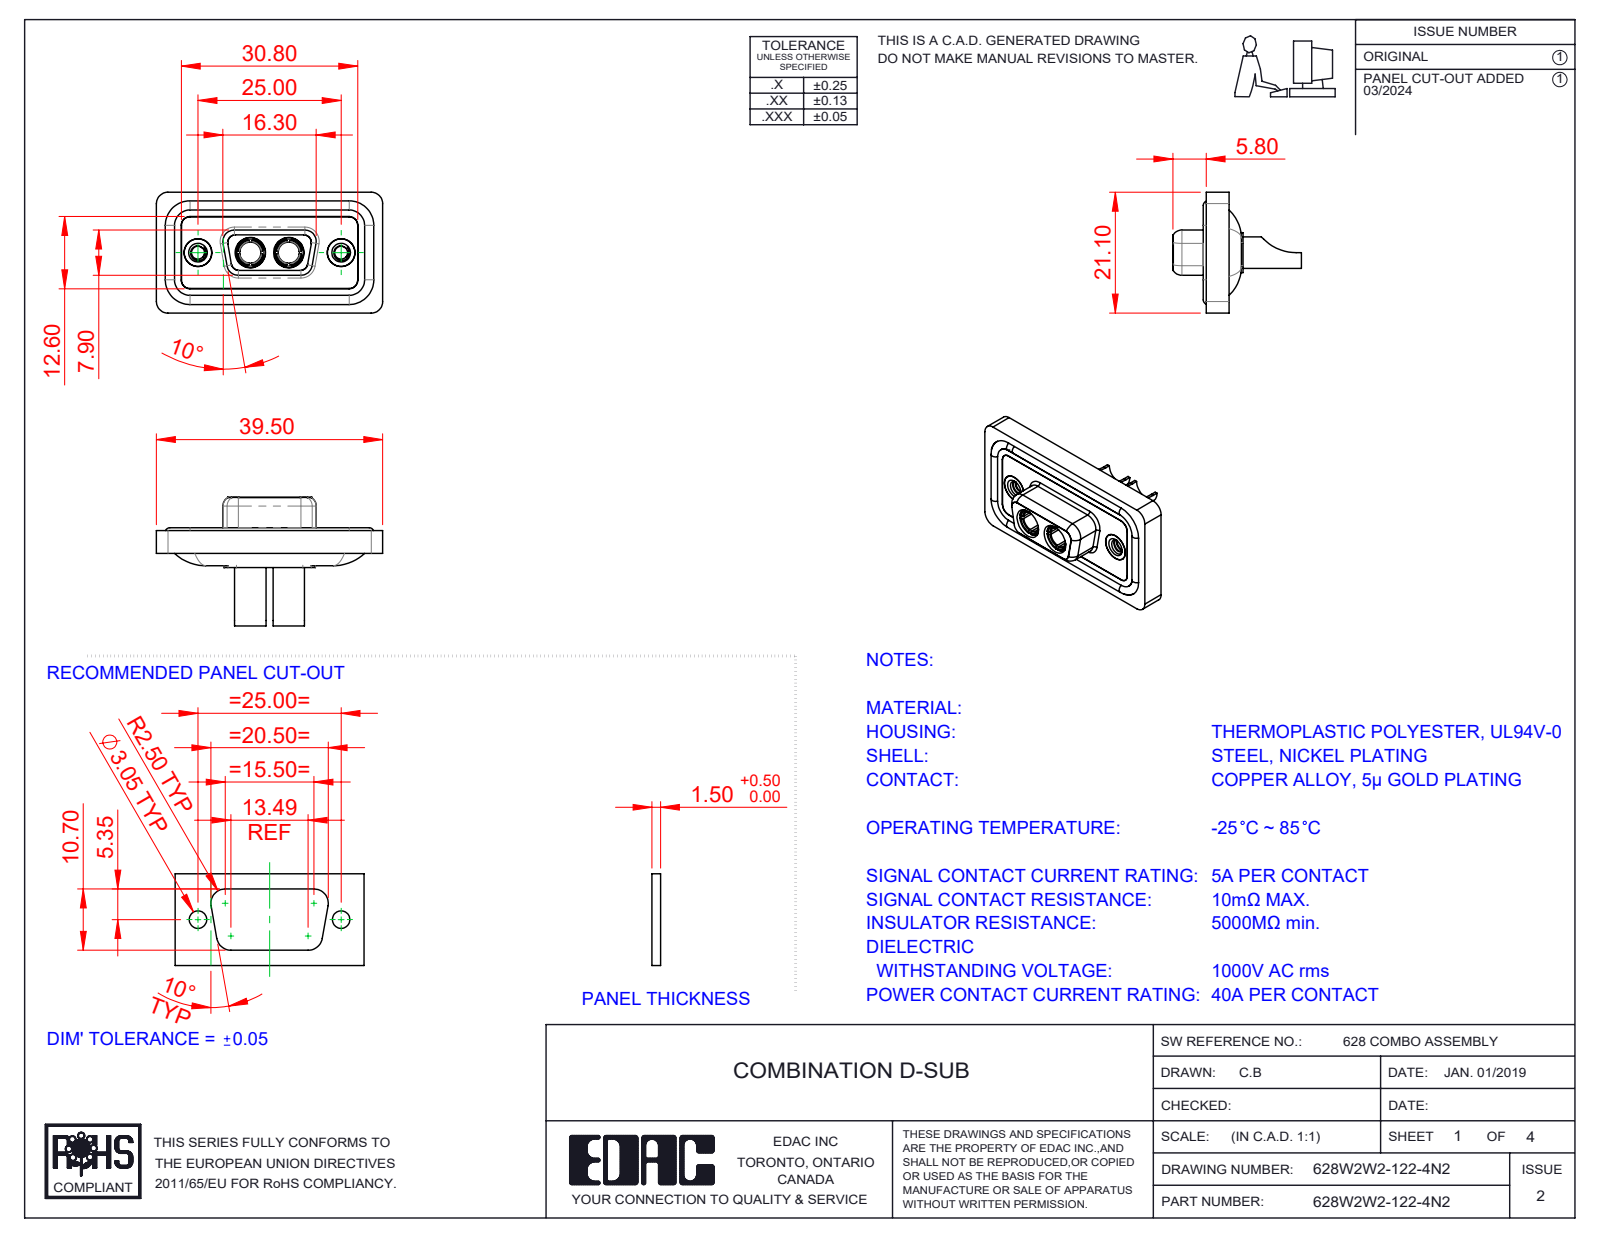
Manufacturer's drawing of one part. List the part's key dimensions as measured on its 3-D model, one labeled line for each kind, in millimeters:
Part name (STEP PRODUCT): 628Combo Waterproof Housing_09 Contacts; 628Combo Shell Rear_09 Contacts; Power Socket_40A SC; 628Combo Shell Front_09 Contacts (+3 more)
STEP written by: SolidWorks 2023 (CONFIG_CONTROL_DESIGN)
Units: millimetres
Bodies: 11 solids, 540 faces (167 planar, 236 cylindrical, 137 other)
Overall size (bounding box): 39.5 × 22.45 × 21.1
Volume: 4 793 mm³ · Surface area: 7 916 mm²
Round holes (diameter × count): ⌀4.85 ×4, ⌀2.26 ×2, ⌀3.7 ×2, ⌀4 ×2, ⌀4.05 ×2, ⌀4.6 ×2, ⌀5 ×2, ⌀5.3 ×2
Round bosses / shafts (diameter × count): ⌀1.6 ×4, ⌀5.5 ×2, ⌀5.2 ×2, ⌀4.96 ×2, ⌀4.95 ×2, ⌀4.8 ×2, ⌀4.75 ×2, ⌀3.75 ×2
Partial cylindrical surfaces — rounded edges, fillets, slot ends (radius × count): R1.5 ×22, R2 ×18, R1.35 ×8, R1.6 ×8, R0.25 ×4, R0.5 ×4, R0.6 ×4, R0.65 ×4
Main face-to-face distances: 0.4, 1.1, 2.9, 1.8, 0.5, 1.6, 5.65, 7.45, 5.35, 3.1
Hole centre spacings: 9.14, 15.86, 6.72, 25
